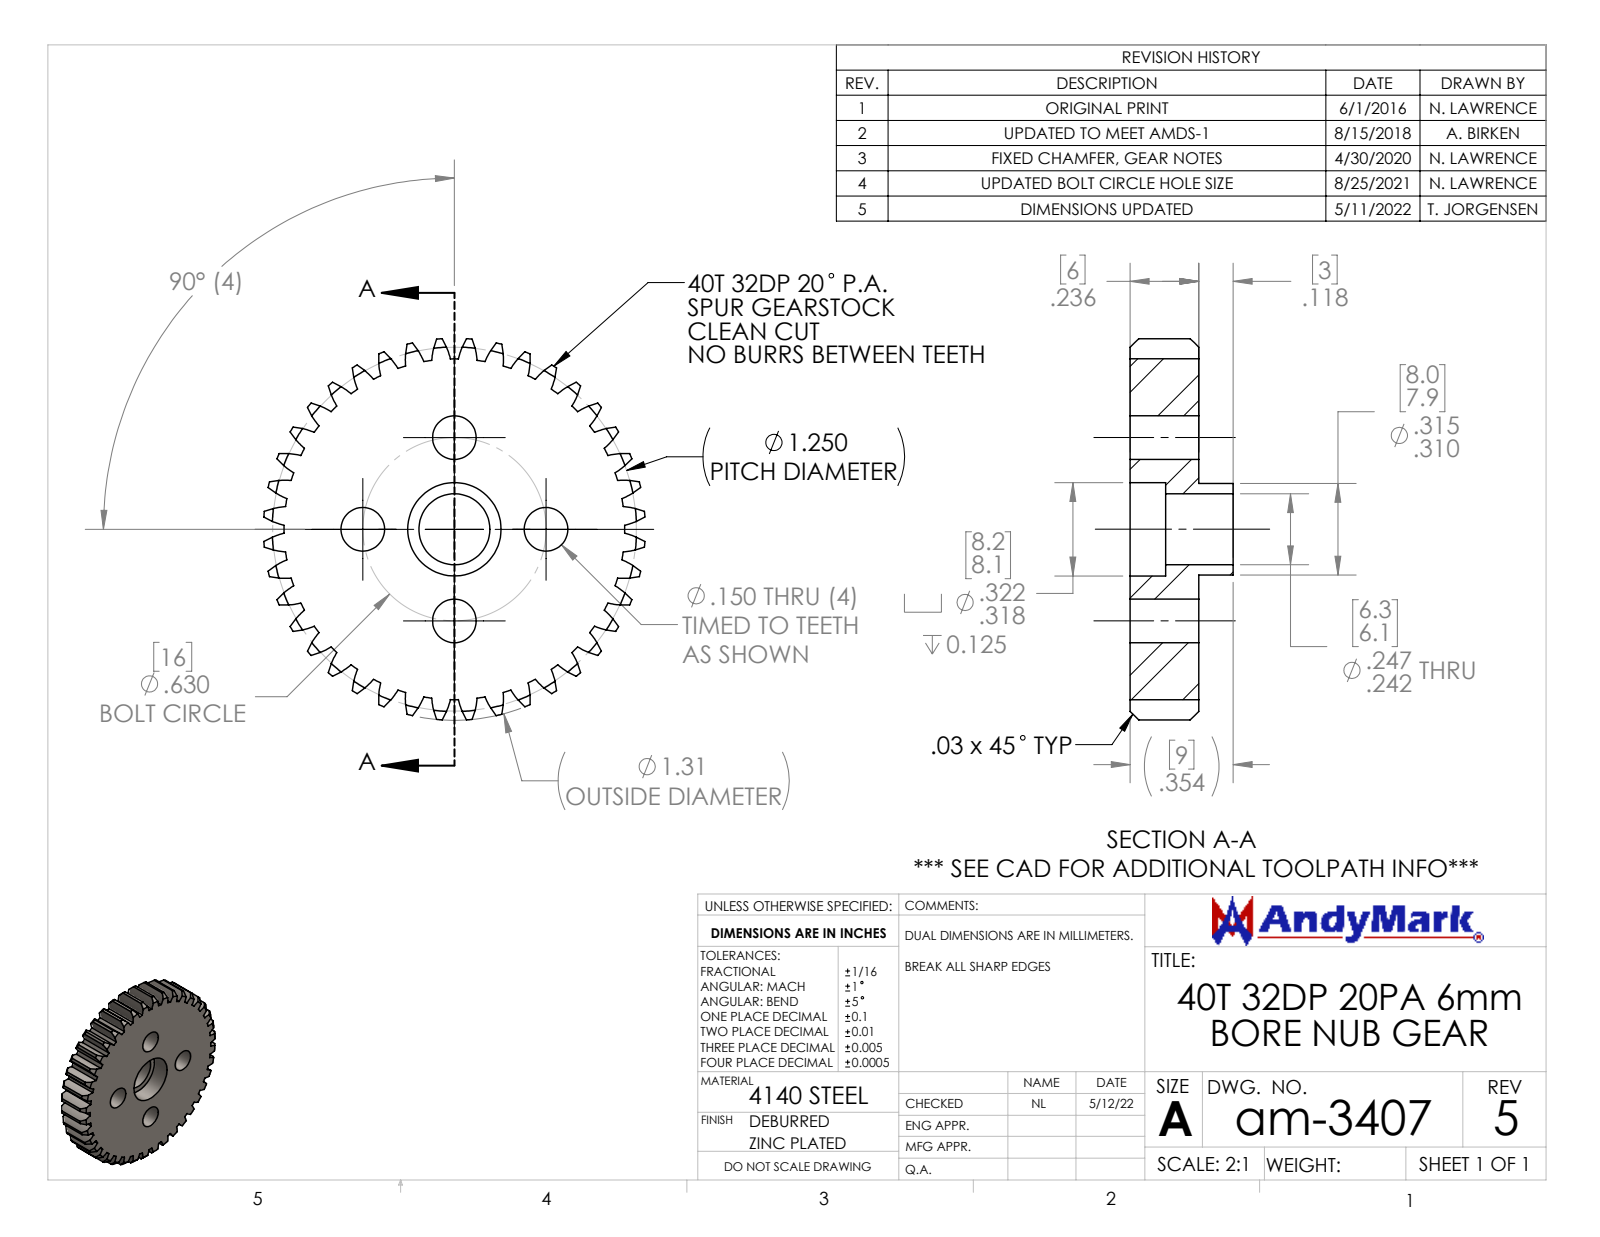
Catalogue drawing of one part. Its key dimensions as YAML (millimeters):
part_name: "40T 32DP 20PA With 6mm Bore Nub Gear"
step_written_by: "SolidWorks 2021 (CONFIG_CONTROL_DESIGN)"
units: millimeters
bodies: {solids: 1, faces: 263, planar: 4, cylindrical: 179, other: 80}
overall_size: [33.3, 33.3, 9]
volume: 4200
surface_area: 3107
round_holes:
  - {diameter: 3.8, count: 4}
  - {diameter: 6.2, count: 1}
  - {diameter: 8.2, count: 1}
round_bosses_or_shafts:
  - {diameter: 8, count: 1}
partial_cylinders:
  - {radius: 6.4, count: 80}
  - {radius: 14.9, count: 1}
  - {radius: 16.7, count: 1}
face_to_face_distances: [6, 2.9, 3.1, 3, 5.9, 9]
hole_center_spacings: [8, 11.3, 16]
